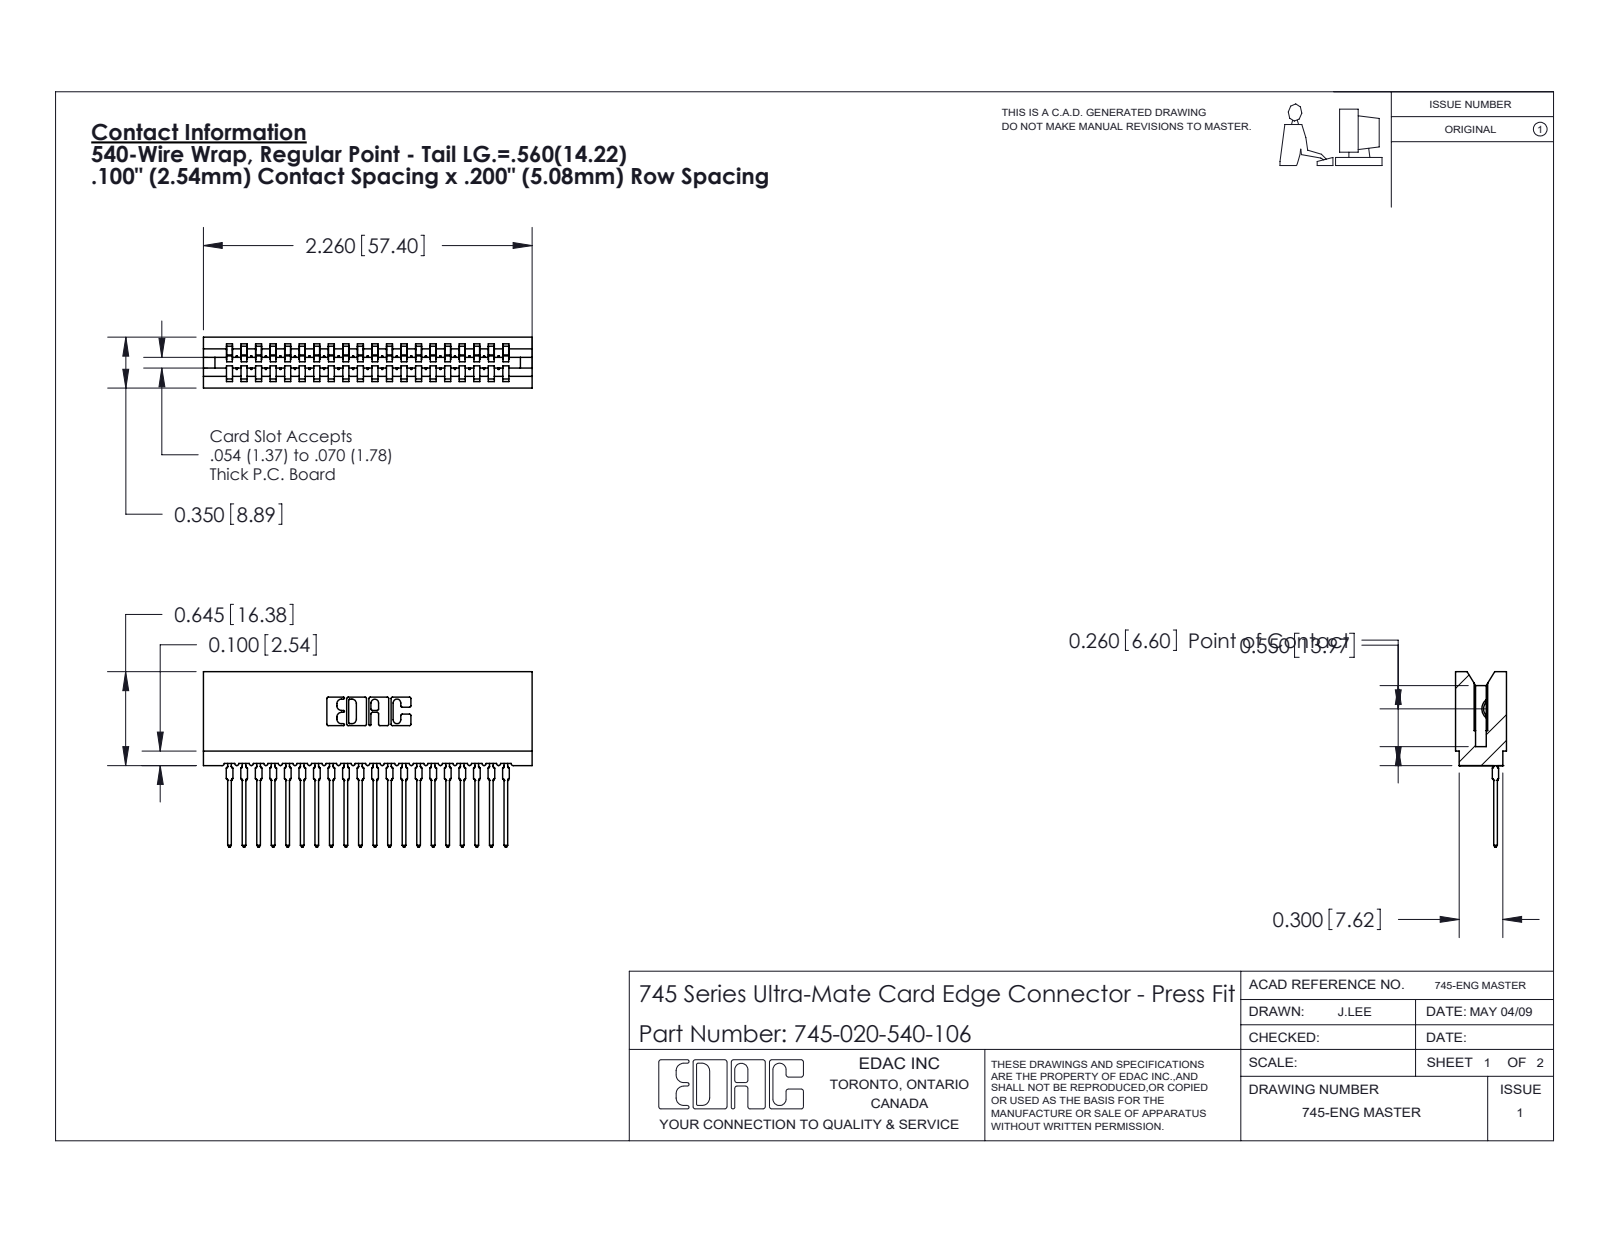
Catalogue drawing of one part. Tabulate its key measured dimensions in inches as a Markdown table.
| quantity | value |
| --- | --- |
| part name | 745-292-001_540; 745-020-540-106; 745 Part_Insulator Option - 06 |
| STEP written by | SolidWorks 2020 (CONFIG_CONTROL_DESIGN) |
| units | inches |
| bodies | 21 solids, 2336 faces (1396 planar, 420 cylindrical, 520 other) |
| overall size | 2.26 × 1.206 × 0.35 |
| volume | 0.314 in³ |
| surface area | 14.56 in² |
| partial cylindrical surfaces (radius × count) | 0.015 × 40, 0.021 × 40, 0.01 × 22, 0.007 × 6, 0.031 × 6, 0.005 × 4, 0.011 × 4, 0.026 × 3 |
| main face-to-face distances | 0.1, 0.2, 0.3, 0.4, 0.5, 0.35, 0.6, 0.7, 0.138, 0.212 |
